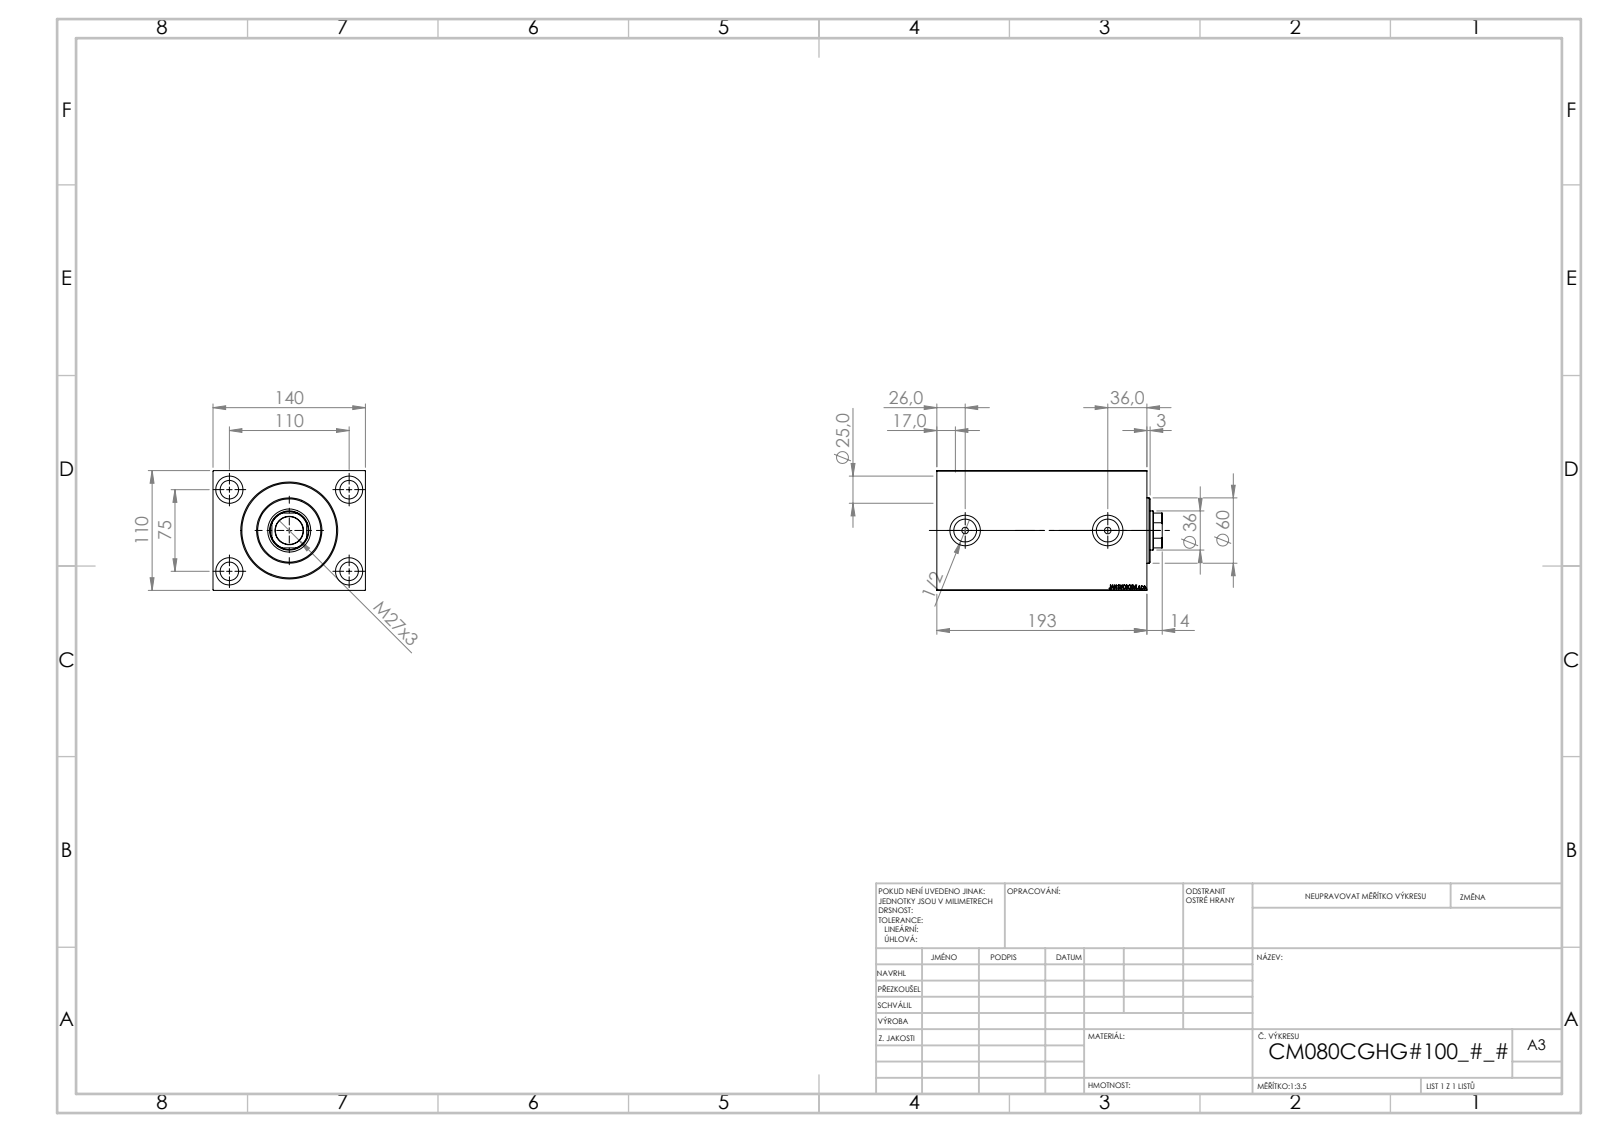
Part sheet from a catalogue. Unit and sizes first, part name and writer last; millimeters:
Units: millimetres
Overall size (bounding box): 207 × 140 × 110
Round holes (diameter × count): ⌀17 ×4, ⌀25 ×4, ⌀6 ×2, ⌀20.96 ×2, ⌀28 ×2, ⌀25.5 ×1, ⌀36 ×1, ⌀39.5 ×1, ⌀80 ×1, ⌀82 ×1, ⌀87 ×1
Round bosses / shafts (diameter × count): ⌀60 ×1
Partial cylindrical surfaces — rounded edges, fillets, slot ends (radius × count): R17.5 ×1
Main face-to-face distances: 110, 140, 193, 172, 21, 179, 14, 158, 100, 114
Hole centre spacings: 66.57, 75, 110, 133.14, 131
Volume: 2 351 000 mm³ · Surface area: 273 130 mm²
Bodies: 3 solids, 865 faces (409 planar, 62 cylindrical, 394 other)
Part name (STEP PRODUCT): V450CM_C_VCP; V450CM_VC_B; V450CM_C_Body
STEP written by: SolidWorks 2019 (CONFIG_CONTROL_DESIGN)
